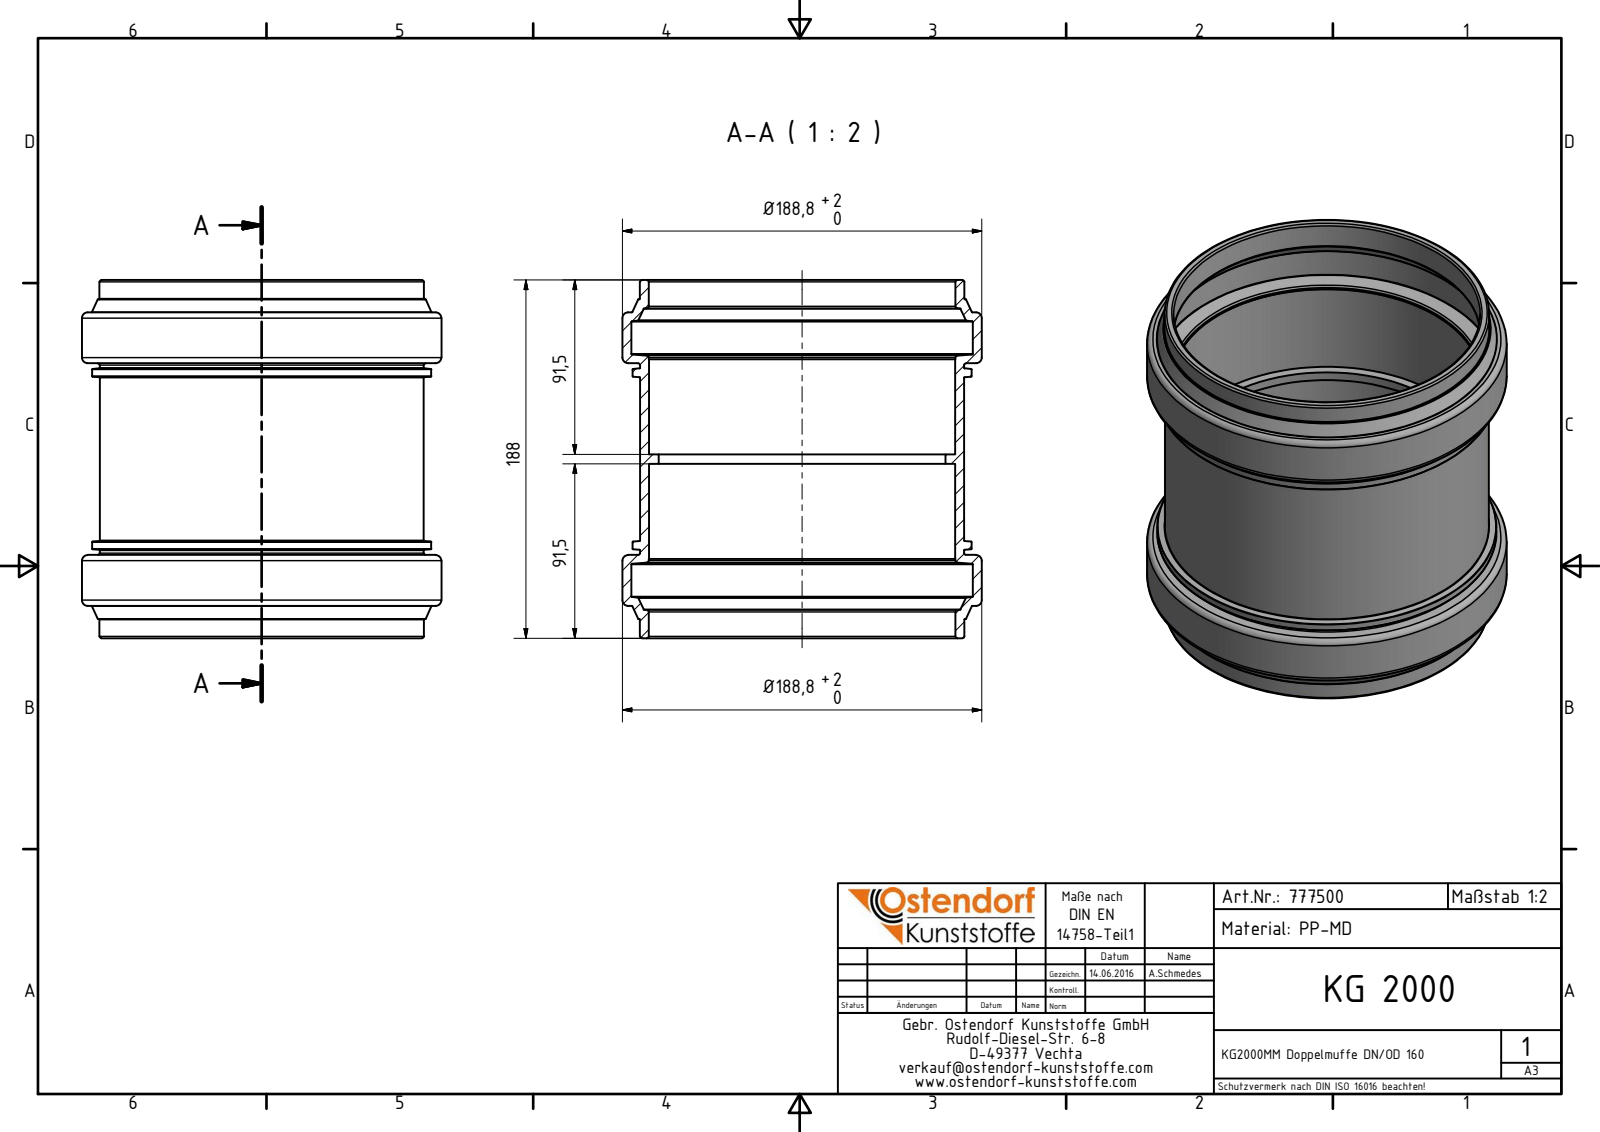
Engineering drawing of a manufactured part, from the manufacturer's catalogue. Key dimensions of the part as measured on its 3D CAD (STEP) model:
Part name (STEP PRODUCT): 777500 KG2000MM Doppelmuffe DN_OD 160
STEP written by: Autodesk Inventor 2016 (AUTOMOTIVE_DESIGN)
Units: millimetres
Bodies: 1 solid, 80 faces (12 planar, 18 cylindrical, 50 other)
Overall size (bounding box): 188.8 × 188.8 × 188
Volume: 577 176 mm³ · Surface area: 247 094 mm²
Round holes (diameter × count): ⌀150.7 ×1, ⌀160.7 ×1, ⌀161 ×1, ⌀179.4 ×1
Round bosses / shafts (diameter × count): ⌀188.8 ×1, ⌀178.1 ×1, ⌀170.4 ×1, ⌀170.1 ×1
Main face-to-face distances: 47.8, 52.8, 100.6, 43.7, 91.5, 96.5, 144.3, 5, 17, 171
